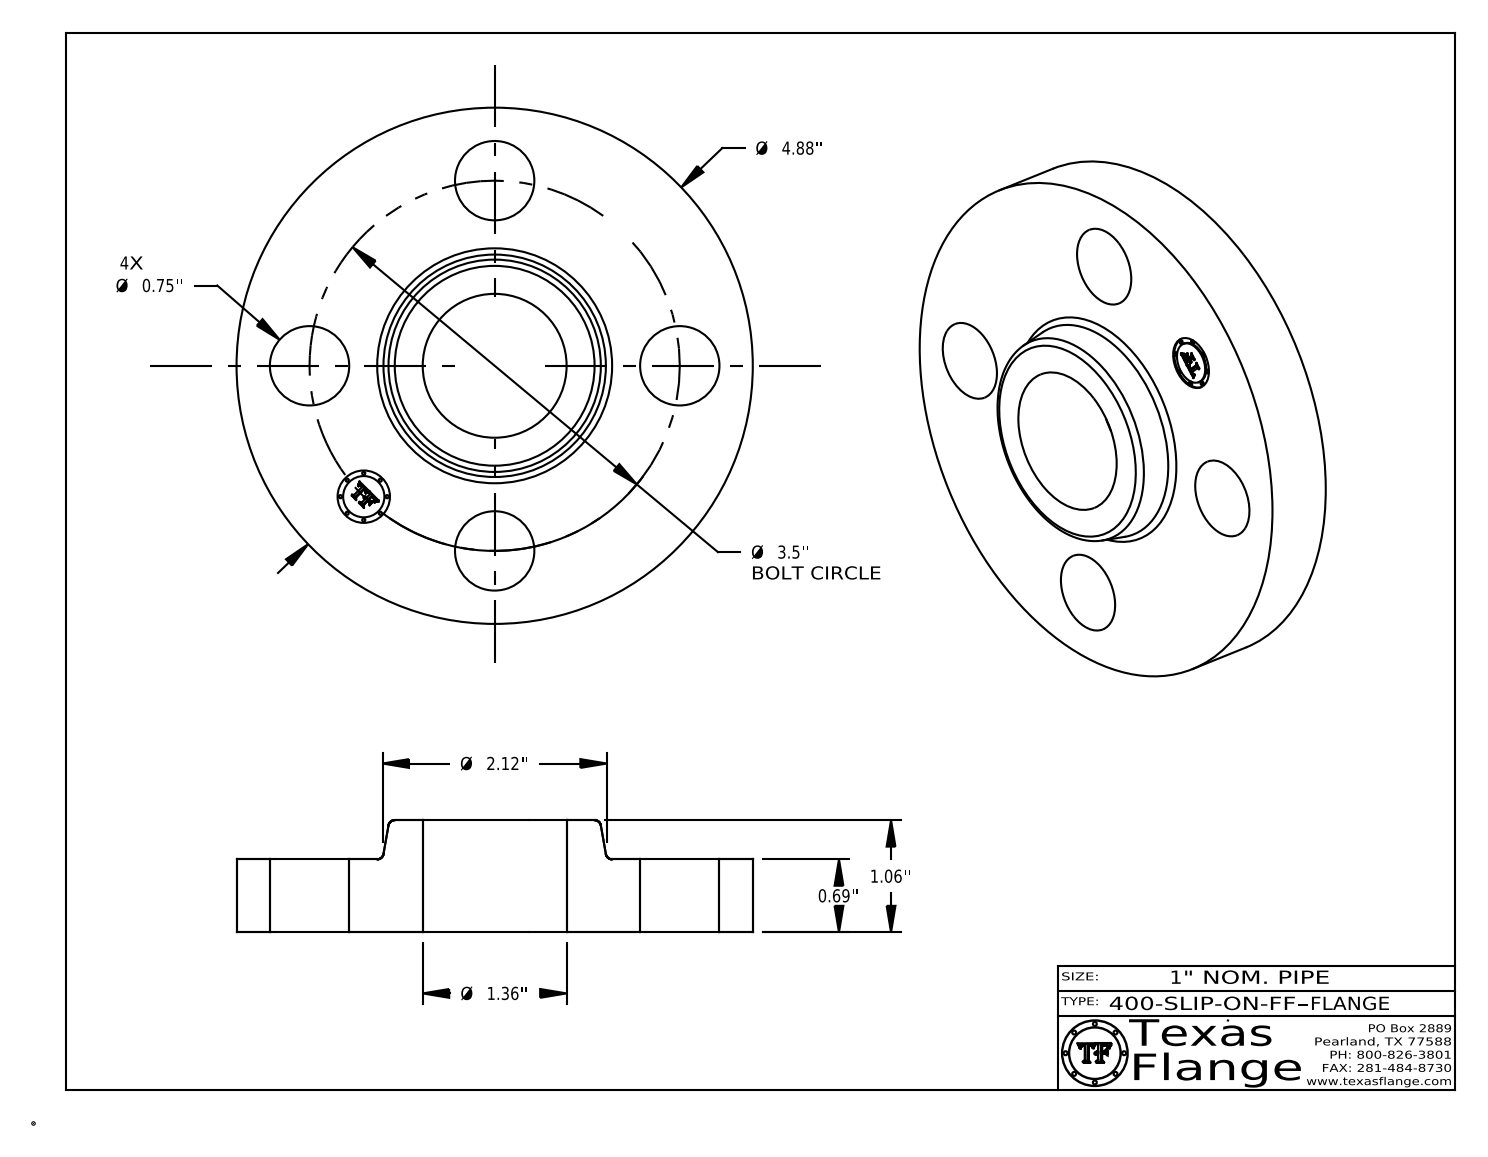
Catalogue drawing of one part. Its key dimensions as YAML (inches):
part_name: "400-SLIP-ON-FF"
step_written_by: "CATIA V5 STEP AP214 (AUTOMOTIVE_DESIGN)"
units: inches
bodies: {solids: 1, faces: 406, planar: 368, cylindrical: 32, other: 6}
overall_size: [4.88, 4.88, 1.06]
volume: 11.37
surface_area: 54.46
round_holes:
  - {diameter: 0.75, count: 4}
  - {diameter: 0.495, count: 1}
  - {diameter: 1.36, count: 1}
round_bosses_or_shafts:
  - {diameter: 0.03, count: 8}
  - {diameter: 4.88, count: 1}
  - {diameter: 0.39, count: 1}
face_to_face_distances: [0.69, 1.06, 0.37, 0.015, 0.675, 0.385, 0.148, 0.145, 0.027, 0.096]
hole_center_spacings: [1.75, 2.475, 1.339, 3.233, 3.5]
